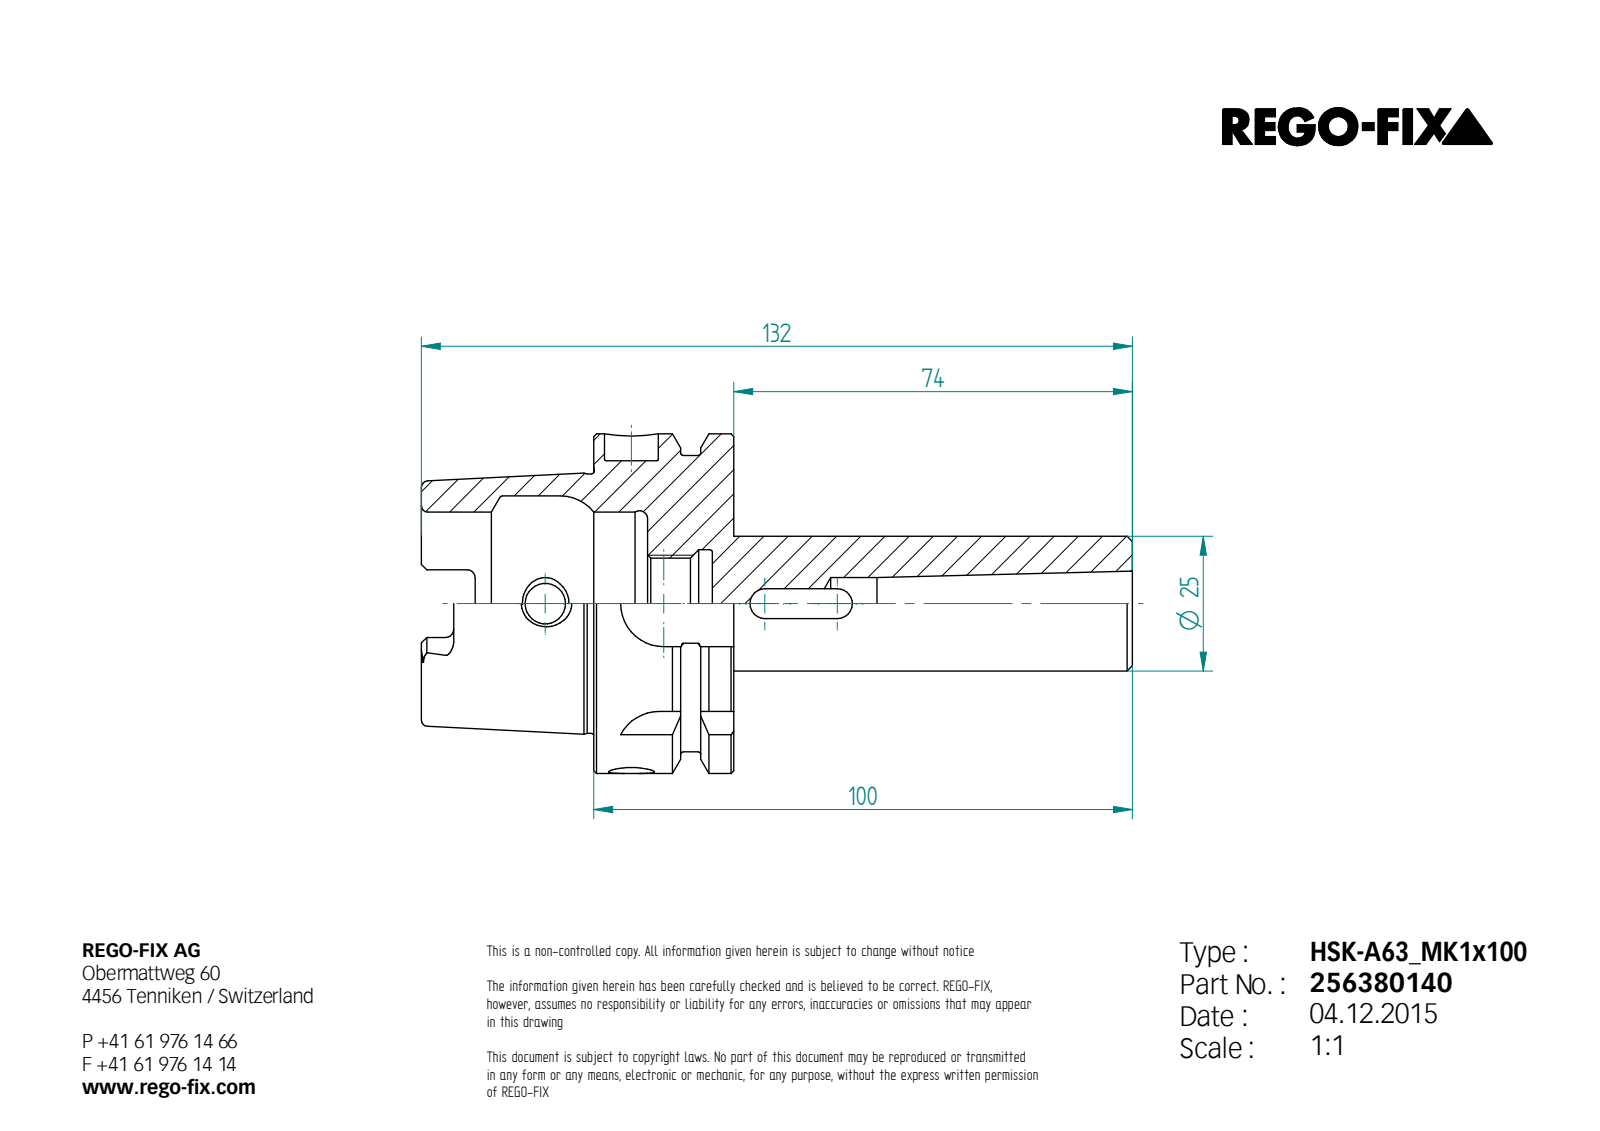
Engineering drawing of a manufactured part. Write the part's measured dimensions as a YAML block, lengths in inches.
step_written_by: "Unknown (AUTOMOTIVE_DESIGN)"
units: inches
bodies: {solids: 1, faces: 129, planar: 46, cylindrical: 35, other: 48}
overall_size: [5.197, 2.48, 2.48]
volume: 6.727
surface_area: 47.51
round_holes:
  - {diameter: 0.295, count: 1}
  - {diameter: 0.335, count: 1}
  - {diameter: 0.382, count: 1}
  - {diameter: 0.394, count: 1}
  - {diameter: 0.666, count: 1}
  - {diameter: 0.787, count: 1}
  - {diameter: 1.339, count: 1}
  - {diameter: 1.575, count: 1}
round_bosses_or_shafts:
  - {diameter: 2.48, count: 1}
  - {diameter: 2.165, count: 1}
  - {diameter: 1.895, count: 1}
  - {diameter: 0.984, count: 1}
partial_cylinders:
  - {radius: 0.059, count: 6}
  - {radius: 0.113, count: 4}
  - {radius: 0.315, count: 4}
  - {radius: 0.109, count: 2}
face_to_face_distances: [1.024, 0.394, 0.63, 1.26, 0.866, 0.157, 0.472, 1.654, 2.283, 0.218]
